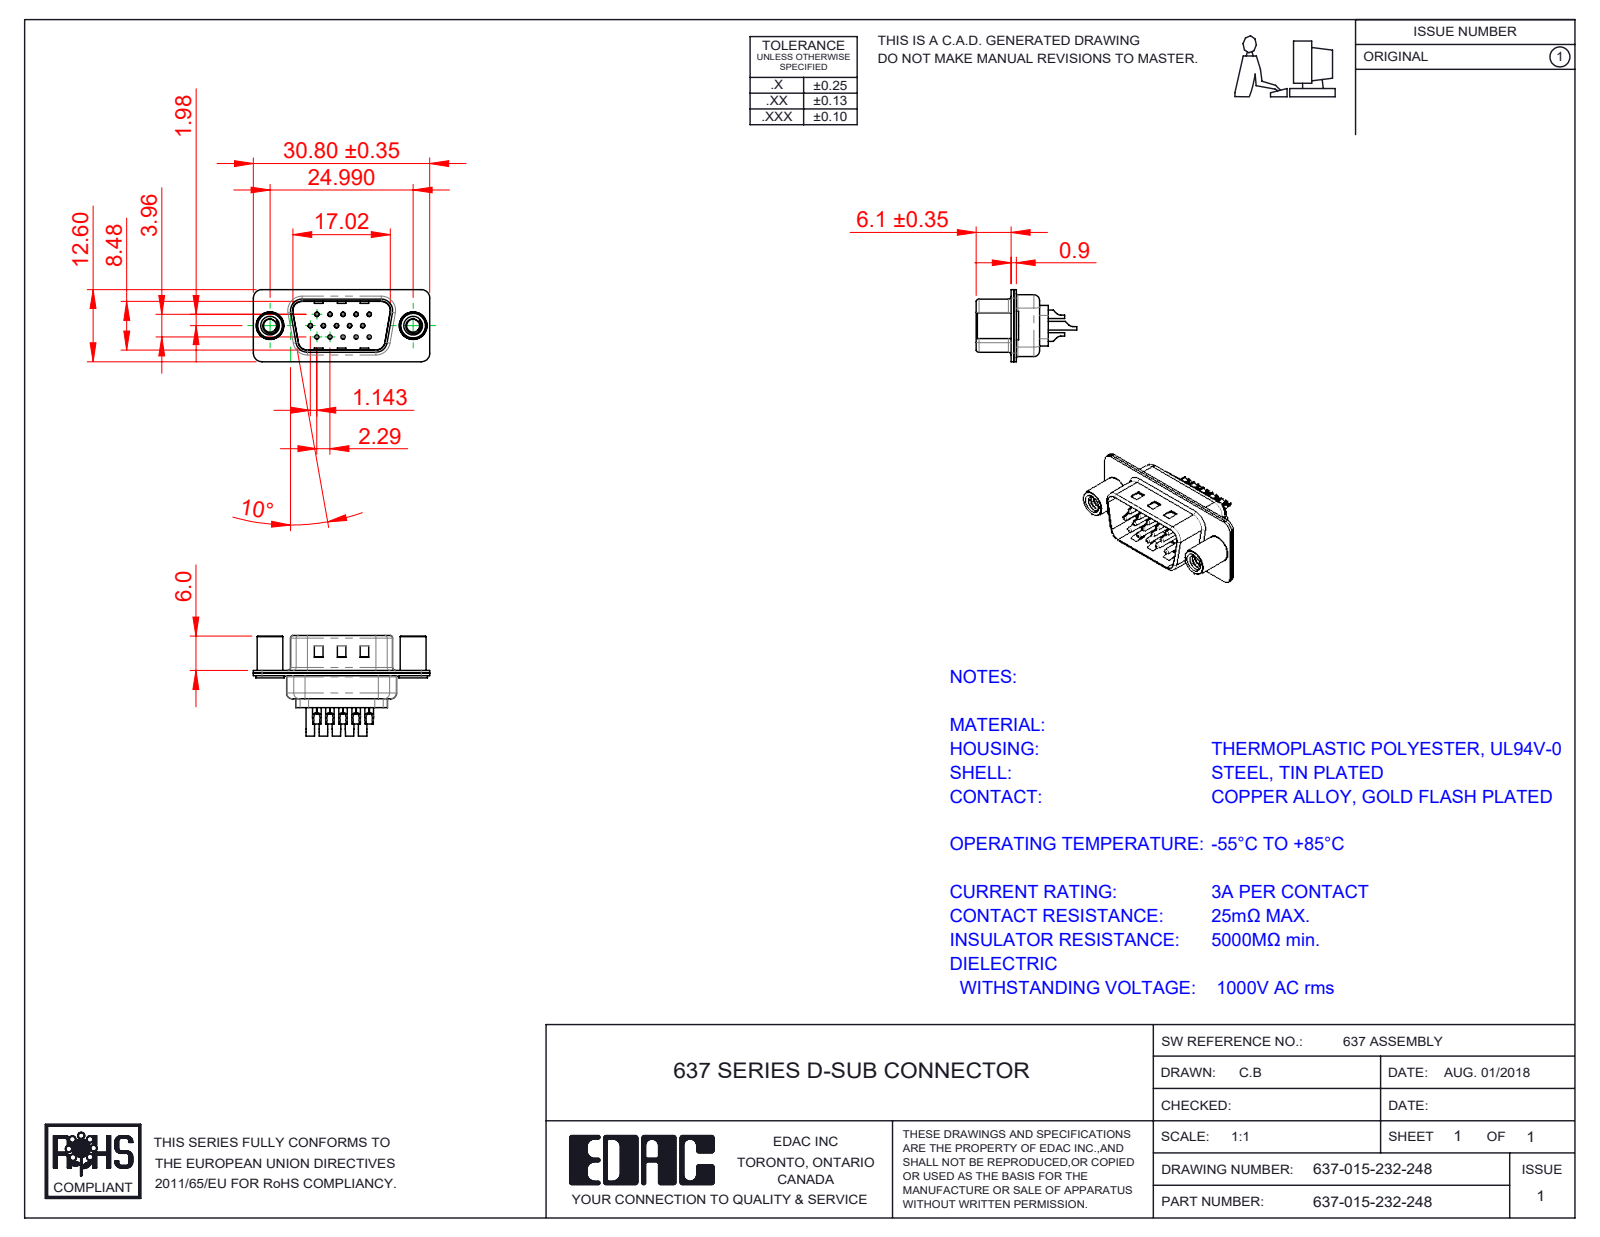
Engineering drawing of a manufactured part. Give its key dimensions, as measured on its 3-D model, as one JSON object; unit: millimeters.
{"part_name": "637 Shell Rear_15 Contacts; 637 Shell Front_15 Contacts; 637 Contact Row 2_32; 637-015-232-248 (+4 more)", "step_written_by": "SolidWorks 2020 (CONFIG_CONTROL_DESIGN)", "units": "millimeters", "bodies": {"solids": 20, "faces": 1298, "planar": 319, "cylindrical": 592, "other": 387}, "overall_size": [30.8, 17.55, 12.6], "volume_mm3": 1394, "surface_area_mm2": 4972, "round_holes": [[0.35, 15], [1.1, 15], [1.6, 15], [2.26, 2], [4, 2], [4.8, 2]], "round_bosses_or_shafts": [[2, 15], [1.5, 15], [0.75, 15], [5, 2], [4.9, 2], [4.5, 2]], "partial_cylinders_radius": [[1.5, 16], [2, 12], [0.5, 8], [1, 7], [0.25, 4], [0.55, 4], [0.7, 4], [0.95, 4]], "face_to_face_distances": [0.45, 0.9, 0.4, 0.7, 8.88, 8.48, 1.05, 0.31, 4.55, 1.16], "hole_center_spacings": [3.96, 2.28, 4.57, 2.29, 6.05, 6.86, 7.92, 6.04]}
